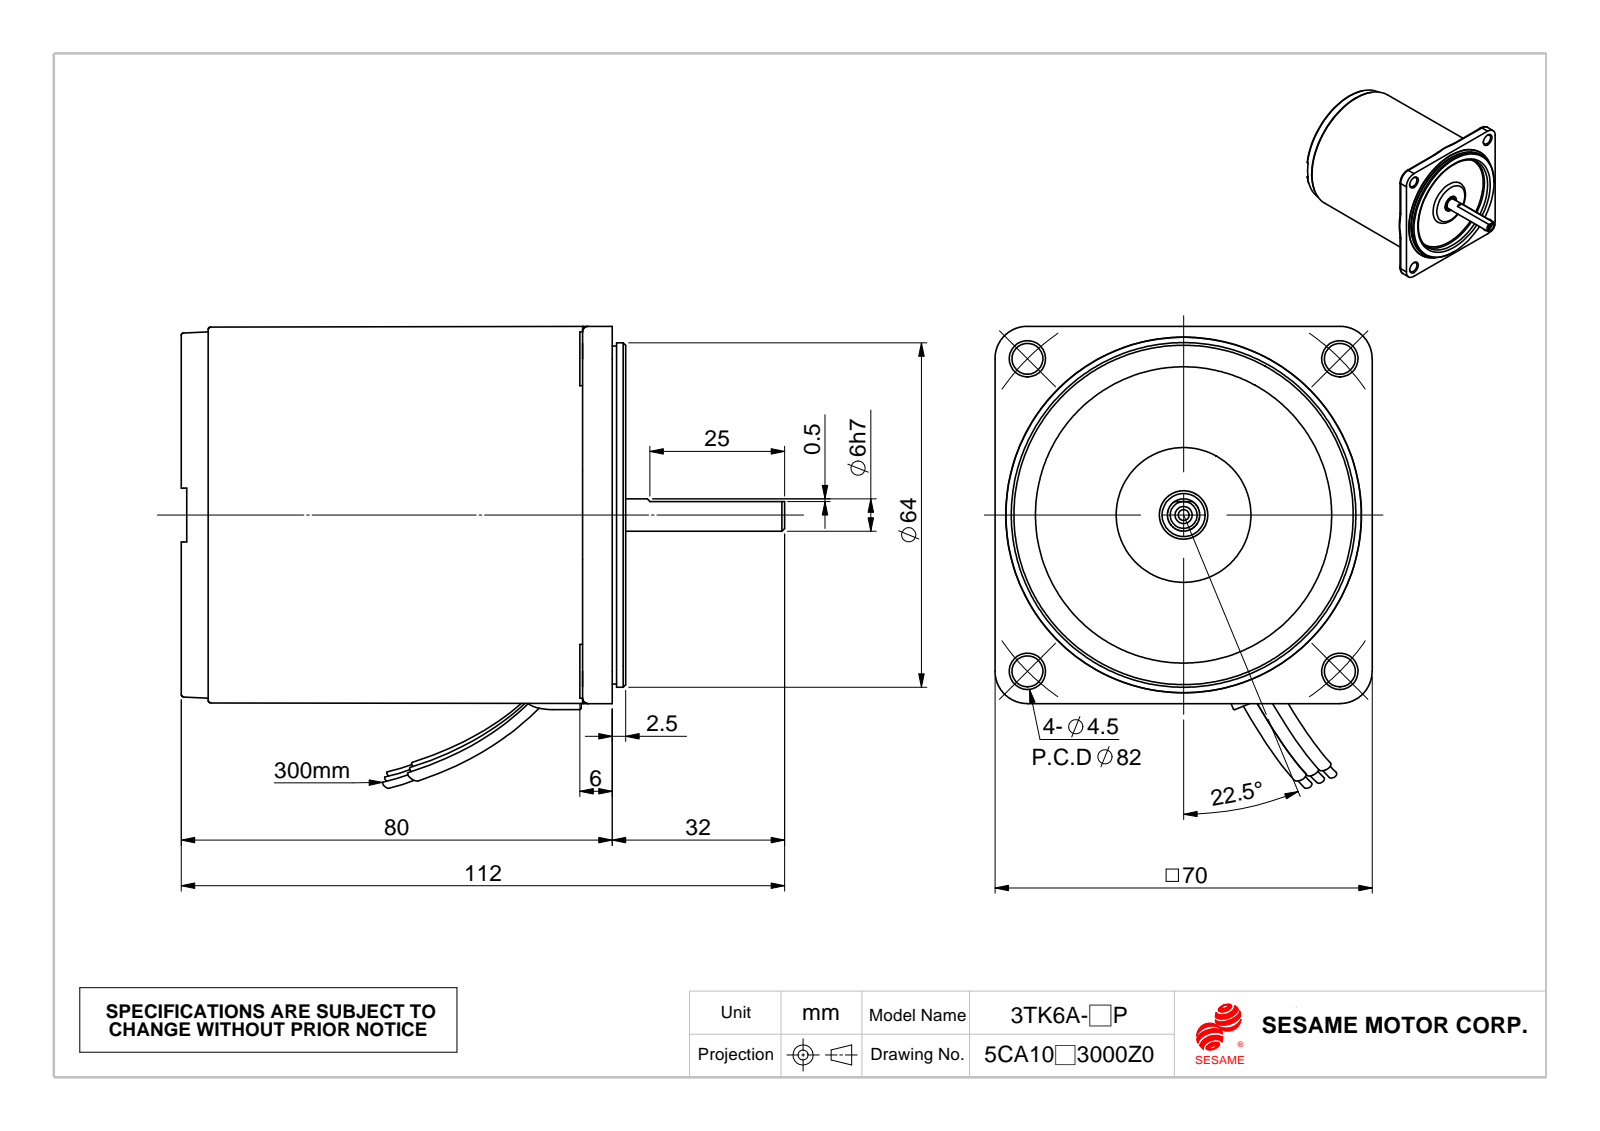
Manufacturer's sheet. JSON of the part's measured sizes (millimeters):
{"part_name": "M315_2車工; C364_車工(成品); 15A_0.成品; 線扣", "step_written_by": "SolidWorks 2010 (CONFIG_CONTROL_DESIGN)", "units": "millimeters", "bodies": {"solids": 7, "faces": 244, "planar": 75, "cylindrical": 78, "other": 91}, "overall_size": [112, 85.74, 70], "volume_mm3": 312248, "surface_area_mm2": 39402, "round_holes": [[5.75, 4], [2, 1], [7.2, 1], [9, 1], [9.5, 1], [18, 1], [55, 1], [58.2, 1], [60.5, 1], [66, 1]], "round_bosses_or_shafts": [[10, 4], [63.93, 1], [62.73, 1], [57.42, 1], [57.2, 1], [9.3, 1], [8, 1], [7.4, 1]], "partial_cylinders_radius": [[0.25, 8], [1, 4], [6, 4], [5.25, 1], [33.98, 1]], "face_to_face_distances": [77.4, 77.5, 1.51, 75.89, 1.61, 1.5, 79, 3.11, 1.6, 4], "hole_center_spacings": [41.01, 58, 82.02]}
